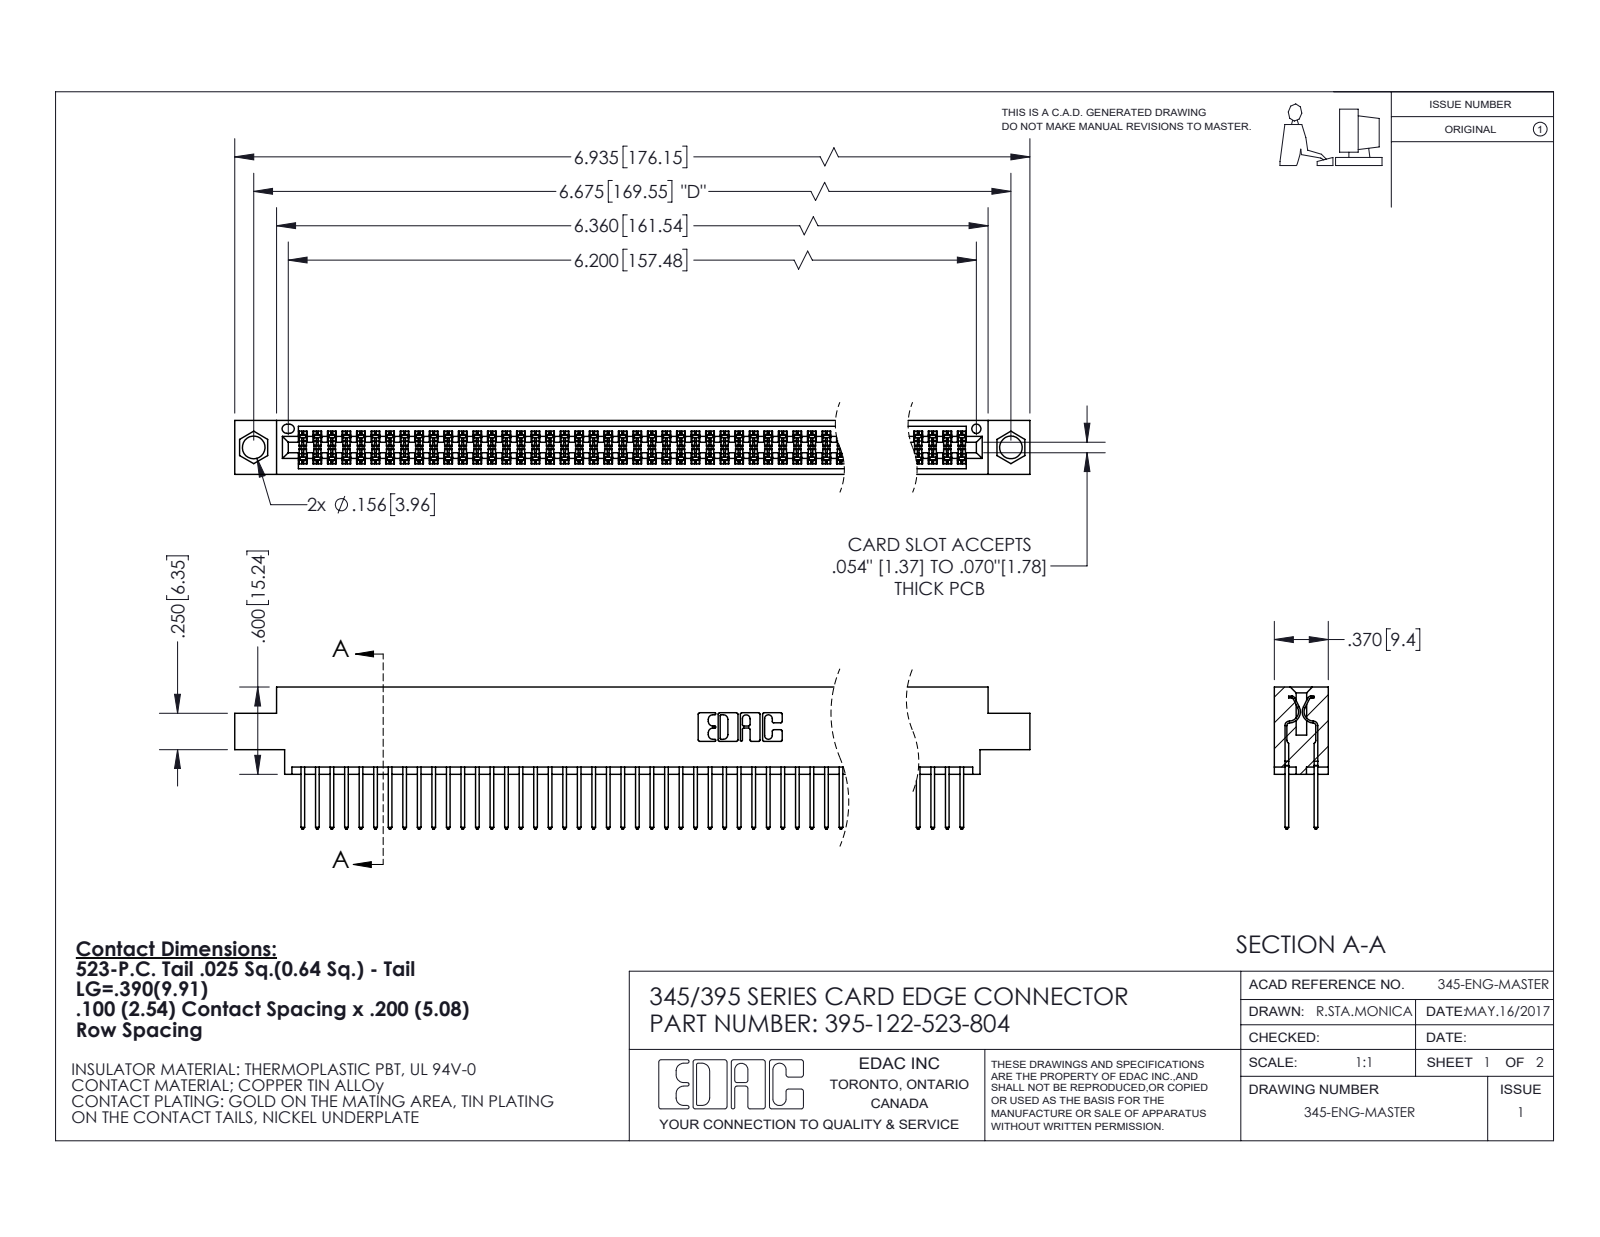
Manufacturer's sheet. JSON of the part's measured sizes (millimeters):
{"part_name": "345-292-001_345-293-123; 395-122-523-804; 345 Part_0.170 Offset - 0.156 Dia-TI", "step_written_by": "SolidWorks 2020 (CONFIG_CONTROL_DESIGN)", "units": "millimeters", "bodies": {"solids": 123, "faces": 6244, "planar": 4124, "cylindrical": 2120, "other": 0}, "overall_size": [176.1, 24.8, 9.4], "volume_mm3": 17320, "surface_area_mm2": 27080, "round_holes": [[4, 2], [1.6, 1]], "partial_cylinders_radius": [[0.2, 183], [0.3, 122], [0.3, 22], [0.2, 6], [0.8, 6], [0.7, 3], [0.4, 2], [0.5, 2]], "face_to_face_distances": [1.8, 7.6, 5.1, 2.5, 6.9, 0.6, 9.4, 5.7, 4.4, 3.8], "hole_center_spacings": [6.9, 163.6, 169.5]}
